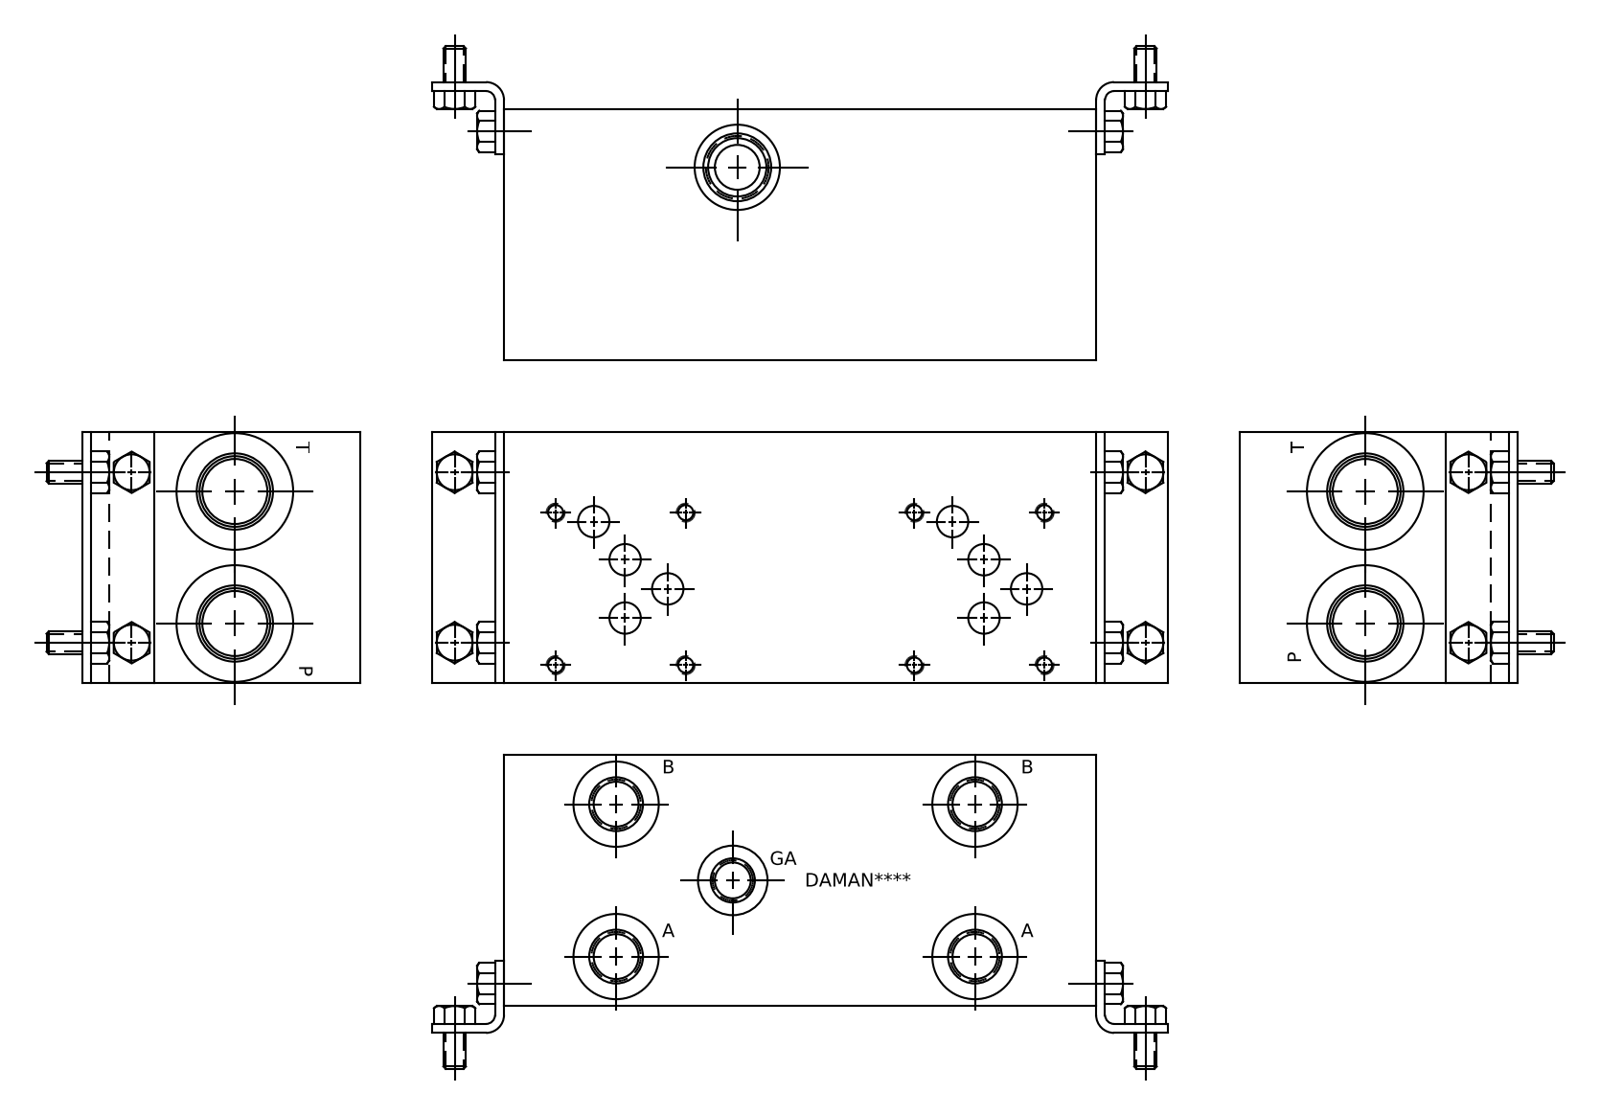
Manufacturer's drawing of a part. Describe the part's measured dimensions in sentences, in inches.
The part is named "Part_AD05P025S_C_3D". Its 3-D file was written by "Autodesk Inventor 2020 (AUTOMOTIVE_DESIGN)". It is 1 solid with 682 faces: 363 planar, 83 cylindrical and 236 other. Overall it measures 8.25 by 3.5 by 3.5 inches. Its volume is 93.31 cubic inches and its surface area 178.3 square inches. Round holes: 8 of diameter 0.201, 8 of diameter 0.25, 8 of diameter 0.438, 4 of diameter 0.625, 4 of diameter 0.689, 4 of diameter 0.75, 4 of diameter 0.758, 4 of diameter 1.206, 2 of diameter 0.257, 2 of diameter 0.312, 2 of diameter 0.906, 2 of diameter 0.981. The main face-to-face distances are 3.5, 0.031, 8.25, 8.219, 3.469, 8.188, 0.75, 0.781, 7.469, 7.438. The hole center spacings are 5, 1.813, 5.433, 2.125, 2.793, 0.546, 0.719, 1.092.
